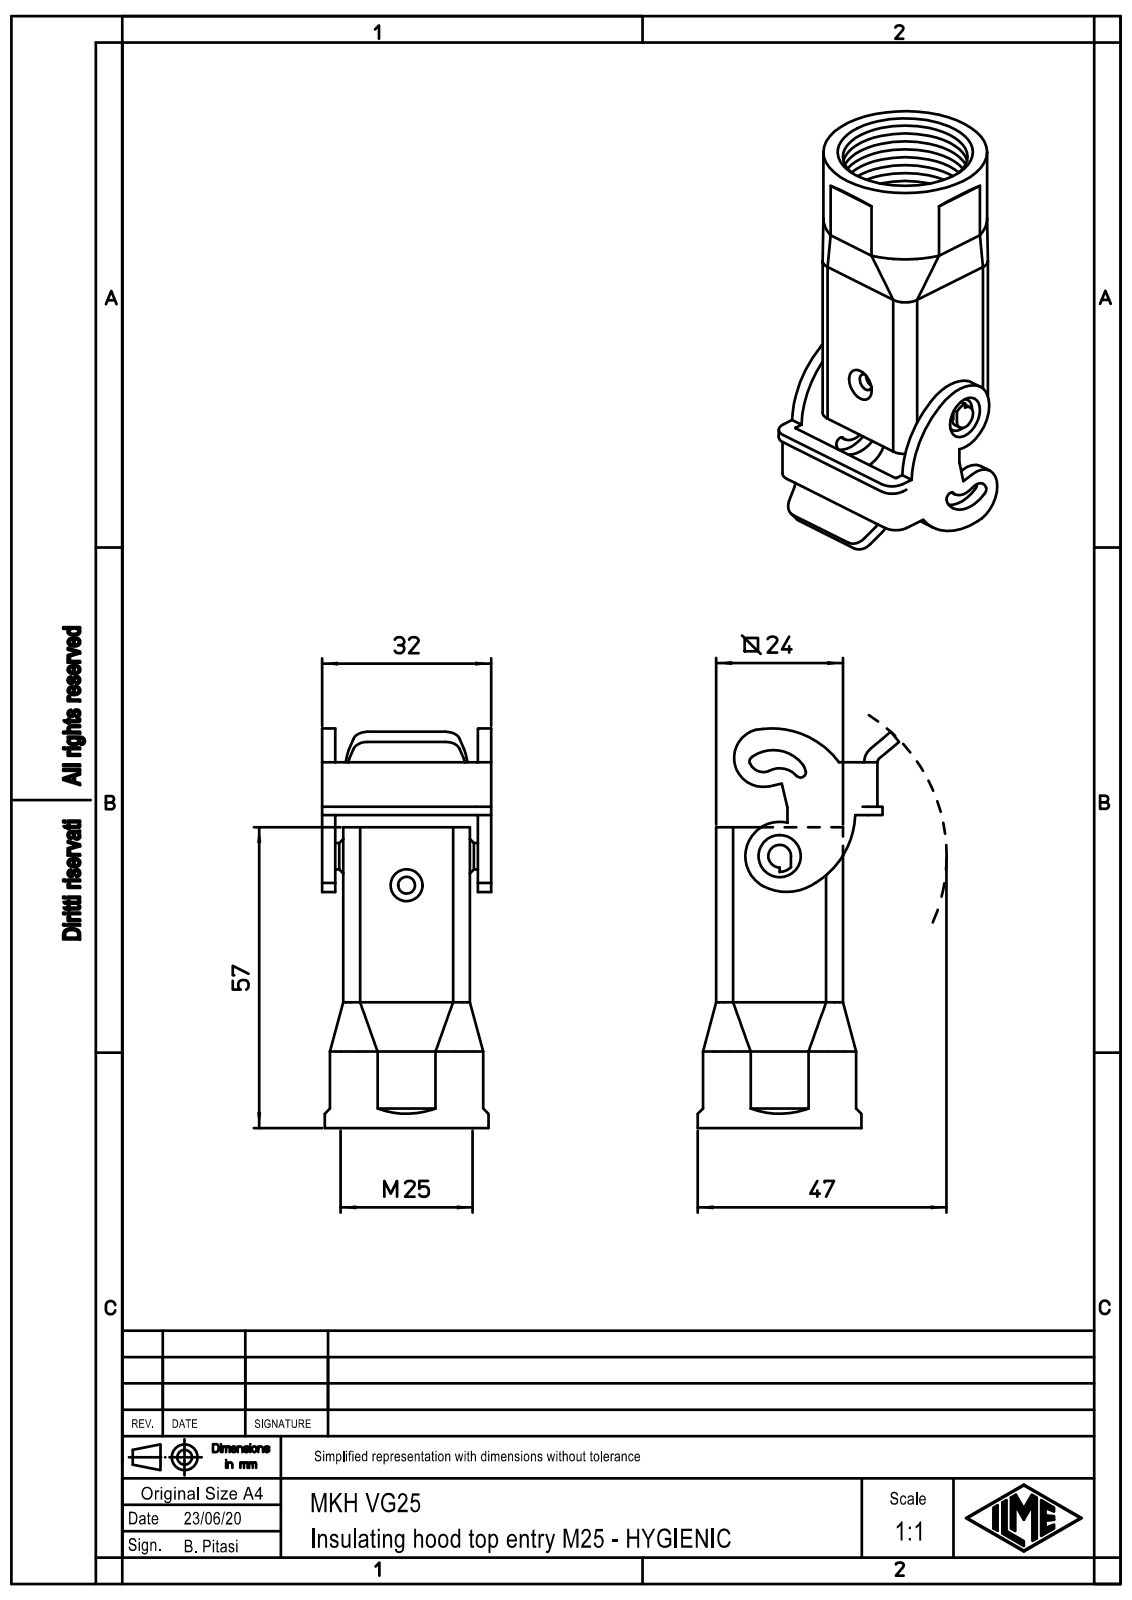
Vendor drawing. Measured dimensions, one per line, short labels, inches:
name: MKH VG25; MKH VG25.stp
written by: Creo Elements/Direct Modeling 20.1B 02-Apr-2019 (C) Parametric Technology GmbH (AUTOMOTIVE_DESIGN)
unit: in
bodies: 1 solid, 144 faces (65 planar, 62 cylindrical, 17 other)
size: 2.98 × 1.502 × 1.26
volume: 0.85 in³; area: 21.92 in²
holes: 1× ⌀0.126, 1× ⌀0.315, 1× ⌀0.929
bosses: 1× ⌀1.22, 1× ⌀0.197, 1× ⌀0.169
rounds: 6× R0.11, 5× R0.126, 4× R0.079, 2× R0.008, 2× R0.039, 1× R0.028, 1× R0.106, 1× R0.118
face distances: 0.098, 1.102, 0.059, 0.157, 0.945, 1.004, 1.161, 1.201, 1.043, 1.063
